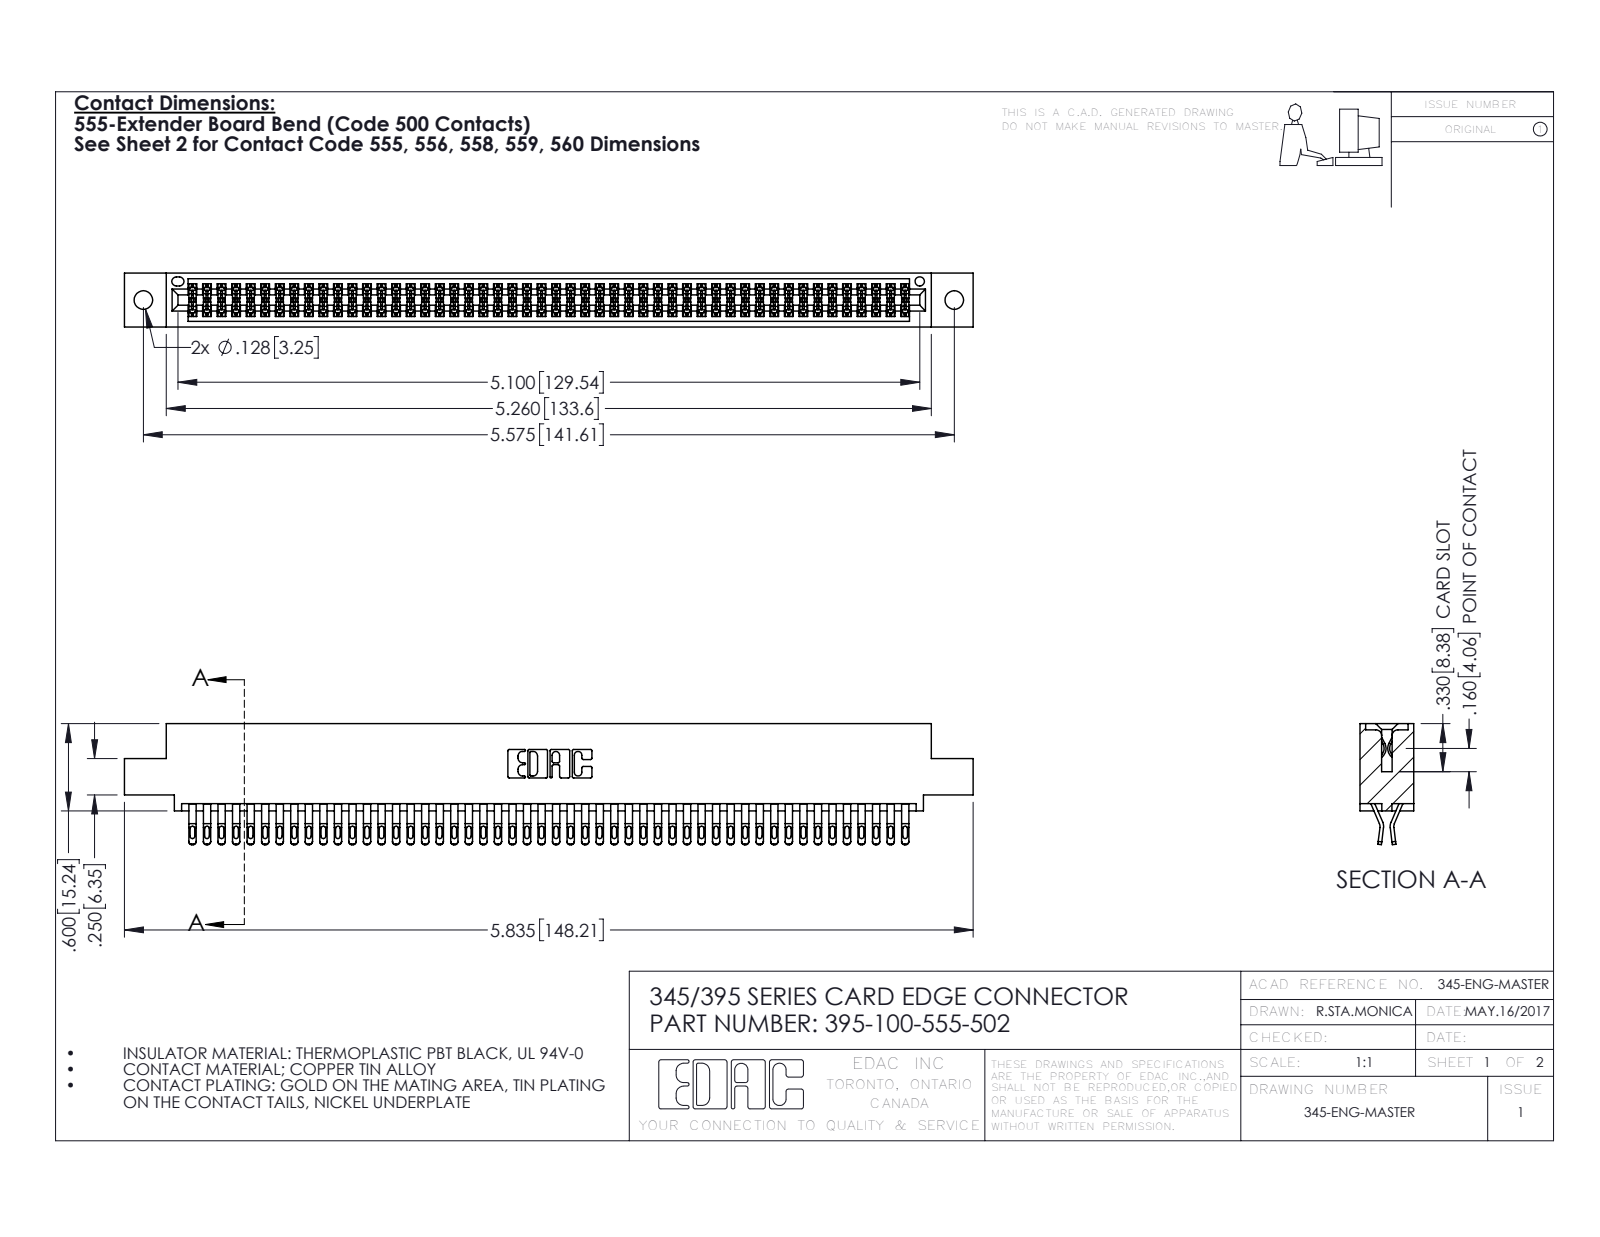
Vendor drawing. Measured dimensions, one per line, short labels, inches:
name: 345-292-001_555 Tail; 345 Part_0.110 Offset - 0.128 Dia; 395-100-555-502
written by: SolidWorks 2016 (CONFIG_CONTROL_DESIGN)
unit: in
bodies: 101 solids, 5730 faces (3184 planar, 2546 cylindrical, 0 other)
size: 5.835 × 0.832 × 0.37
volume: 0.894 in³; area: 35.09 in²
holes: 2× ⌀0.128, 1× ⌀0.064
rounds: 250× R0.016, 200× R0.02, 150× R0.006, 22× R0.01, 6× R0.007, 6× R0.031, 3× R0.026, 2× R0.01
face distances: 0.298, 0.072, 0.025, 0.37, 0.2, 0.098, 0.272, 0.225, 0.175, 0.149
hole spacings: 0.27, 5.339, 5.575
